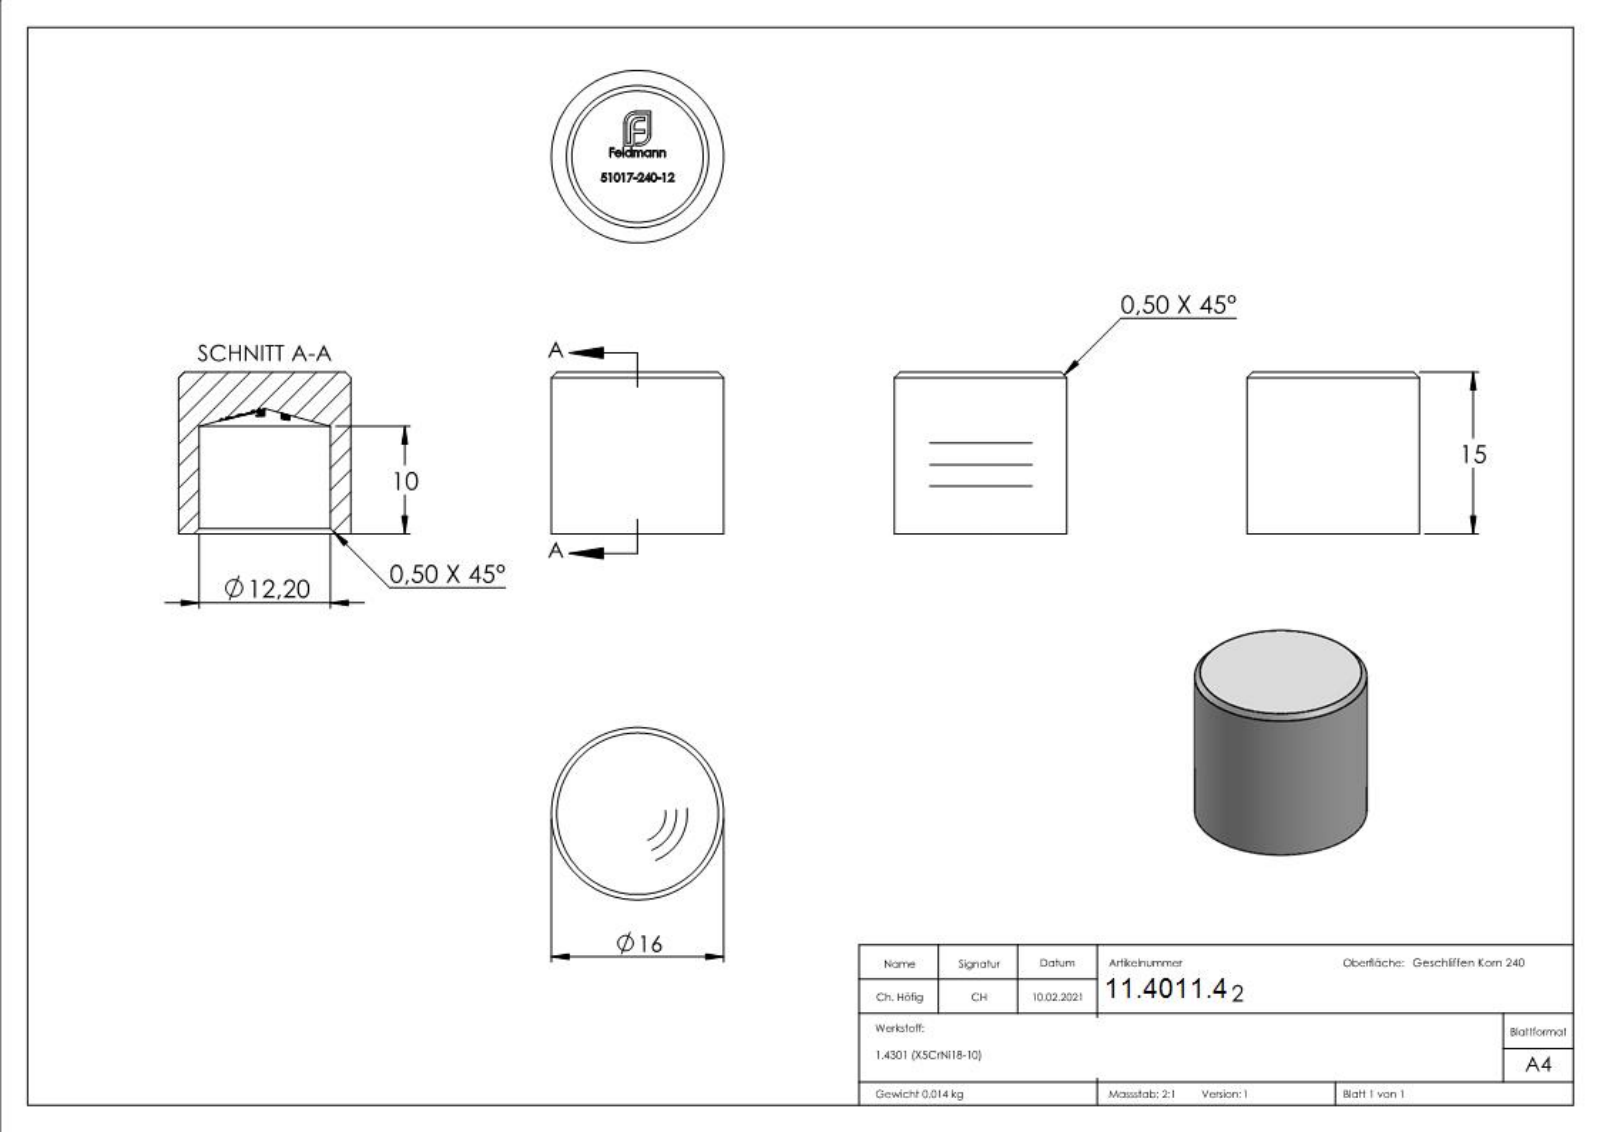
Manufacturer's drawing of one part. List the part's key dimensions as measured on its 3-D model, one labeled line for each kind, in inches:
Part name (STEP PRODUCT): 51017-240-12
STEP written by: SolidWorks 2018 (CONFIG_CONTROL_DESIGN)
Units: inches
Bodies: 1 solid, 289 faces (139 planar, 4 cylindrical, 146 other)
Overall size (bounding box): 0.63 × 0.63 × 0.591
Volume: 0.108 in³ · Surface area: 2.367 in²
Round holes (diameter × count): ⌀0.48 ×1
Round bosses / shafts (diameter × count): ⌀0.63 ×1
Main face-to-face distances: 0.591, 0.088, 0.074, 0.028, 0.078, 0.025, 0.057, 0.048, 0.051, 0.098
